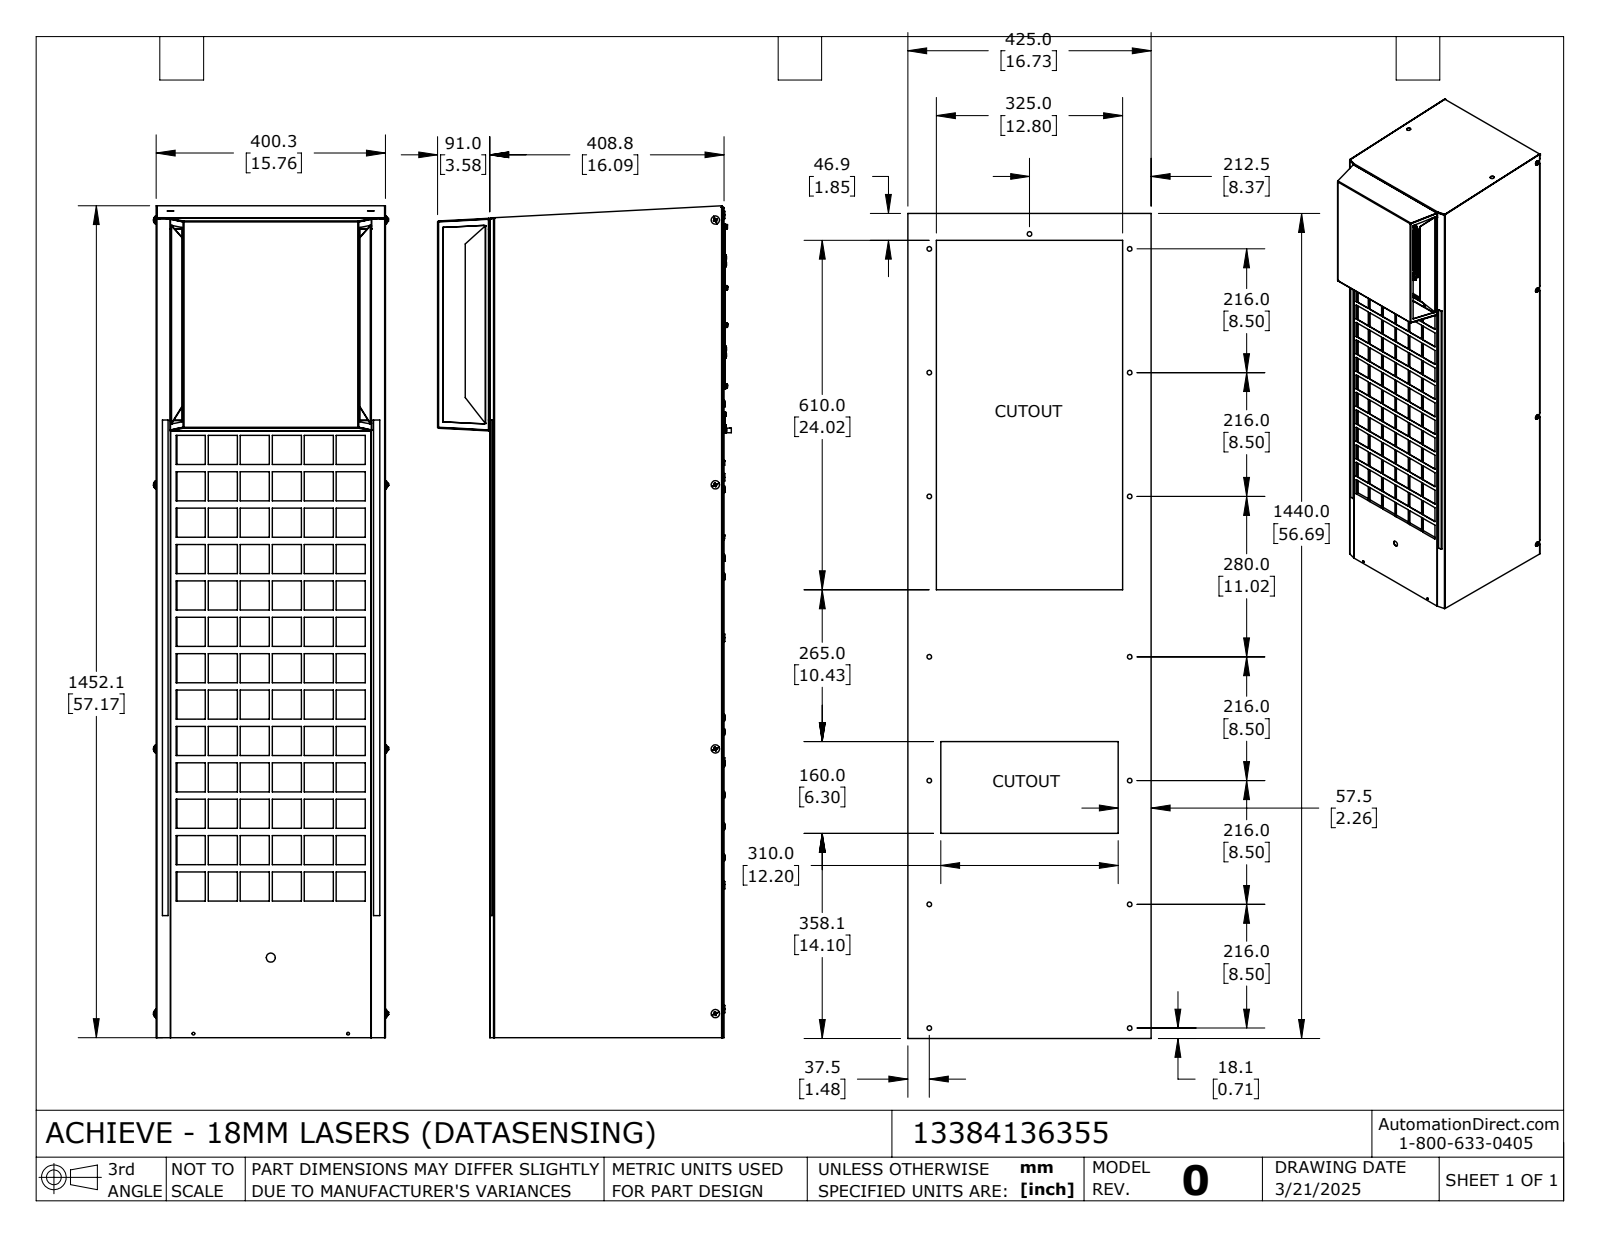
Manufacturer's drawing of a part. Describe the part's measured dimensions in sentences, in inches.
The part is named "13384136355_Default". Its 3-D file was written by "SolidWorks 2024 (CONFIG_CONTROL_DESIGN)". It is 1 solid with 6463 faces: 3532 planar, 1827 cylindrical and 1104 other. Overall it measures 57.171 by 20.19 by 16.113 inches. Its volume is 13 374 cubic inches and its surface area 11 995 square inches. Round holes: 48 of diameter 0.107, 47 of diameter 0.165, 18 of diameter 0.283, 14 of diameter 0.189, 4 of diameter 0.098, 4 of diameter 0.161, 4 of diameter 0.374, 2 of diameter 0.125, 2 of diameter 0.276, 2 of diameter 0.472, 2 of diameter 0.945, 1 of diameter 0.122. Round bosses or shafts: 35 of diameter 0.178, 18 of diameter 0.512, 12 of diameter 0.315, 12 of diameter 0.157, 12 of diameter 0.122, 6 of diameter 0.354, 5 of diameter 0.079, 4 of diameter 0.573. Partial cylindrical surfaces (rounded edges, fillets, slot ends): 352 of radius 0.125, 43 of radius 0.031, 28 of radius 0.076, 18 of radius 0.198, 13 of radius 0.087, 6 of radius 0.132, 5 of radius 0.083, 5 of radius 0.118. The main face-to-face distances are 0.045, 0.045, 0.056, 15.714, 15.759, 15.669, 15.715, 0.28, 0.235, 15.435. The hole center spacings are 7.48, 14.961, 22.441, 3.028, 0.022, 0.037, 7.874, 29.921.
